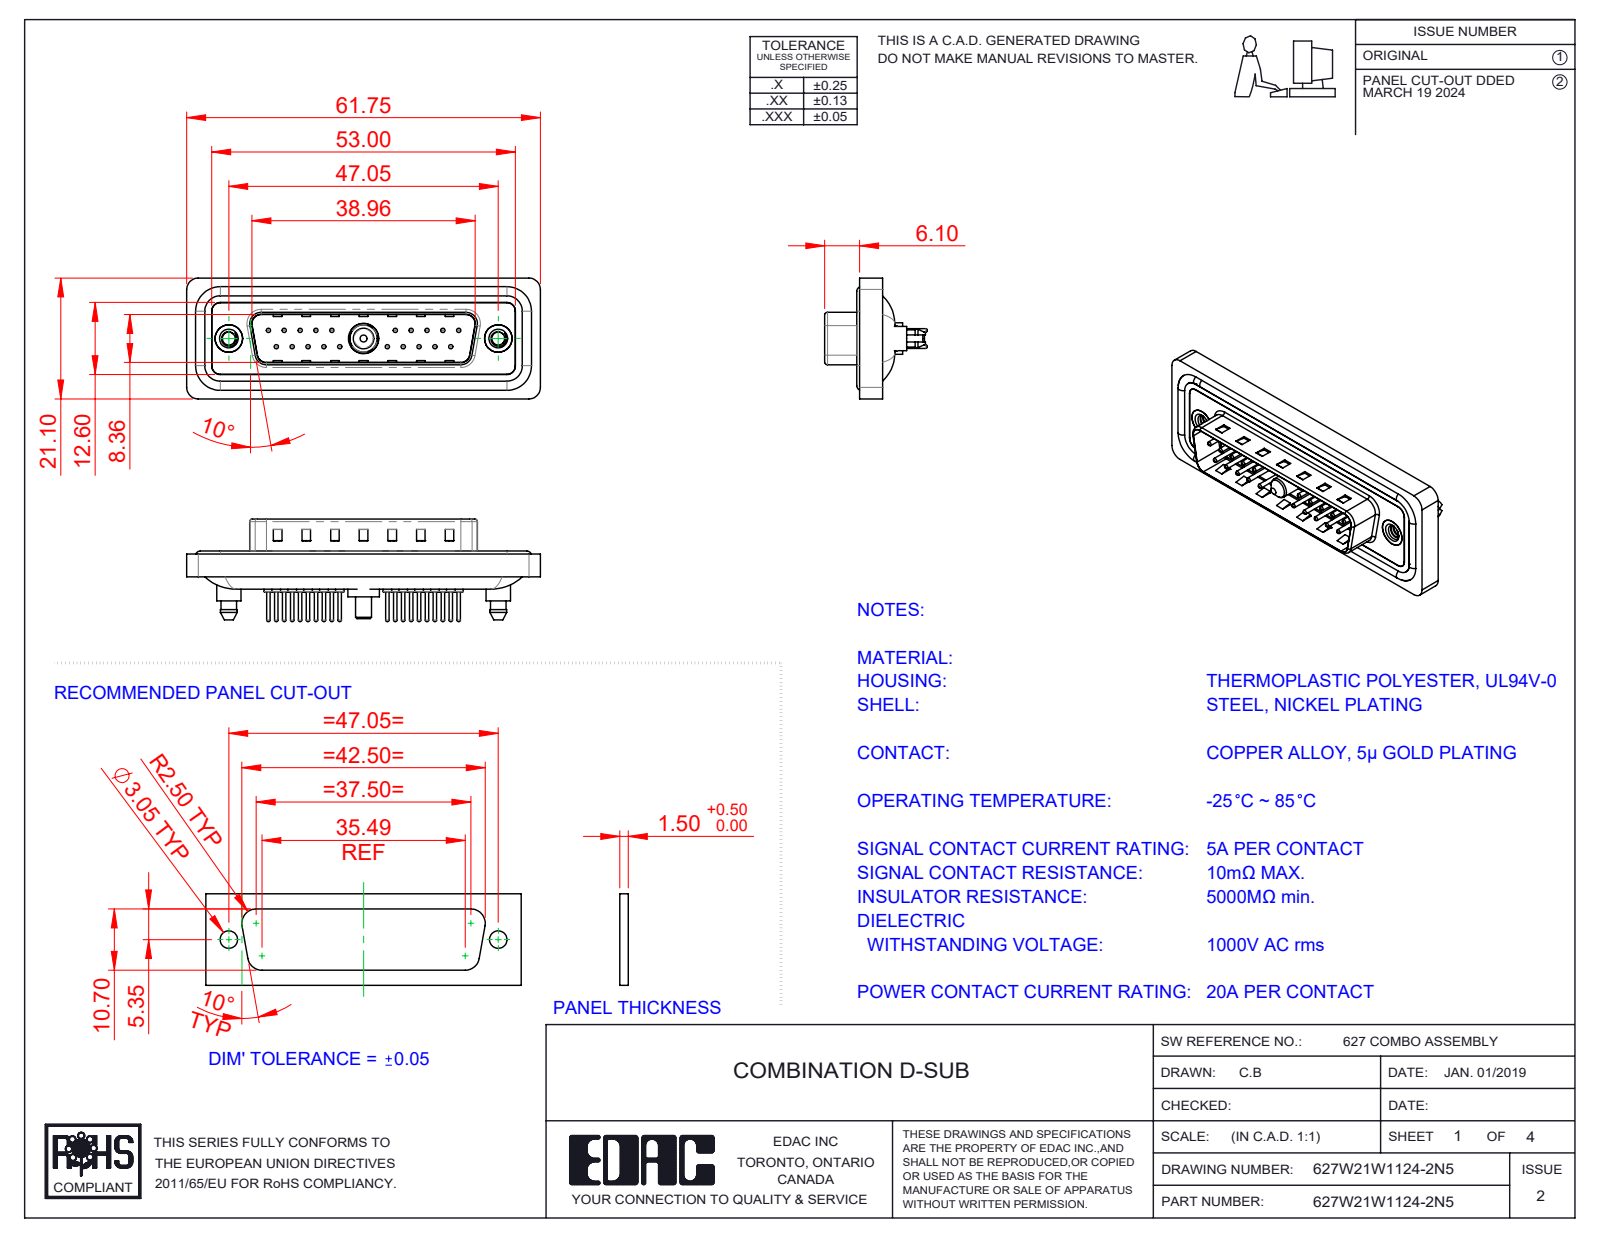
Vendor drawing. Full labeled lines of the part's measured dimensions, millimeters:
Part name (STEP PRODUCT): 627Combo Shell Rear_25 Contacts; Power Pin_20A S; 627Combo Housing_21W1; 627Combo Threaded Boardlock_5 (+5 more)
STEP written by: SolidWorks 2023 (CONFIG_CONTROL_DESIGN)
Units: millimetres
Bodies: 29 solids, 1312 faces (375 planar, 519 cylindrical, 418 other)
Overall size (bounding box): 61.75 × 21.1 × 17.9
Volume: 7 331 mm³ · Surface area: 12 286 mm²
Round holes (diameter × count): ⌀0.75 ×20, ⌀1.6 ×20, ⌀2 ×20, ⌀2.26 ×2, ⌀4 ×2, ⌀4.8 ×2, ⌀5 ×2, ⌀4.85 ×1, ⌀5.3 ×1
Round bosses / shafts (diameter × count): ⌀1.5 ×20, ⌀0.6 ×20, ⌀1.6 ×4, ⌀5.4 ×2, ⌀4.9 ×2, ⌀4.25 ×2, ⌀5.5 ×1, ⌀5.2 ×1
Partial cylindrical surfaces — rounded edges, fillets, slot ends (radius × count): R1.5 ×24, R2 ×18, R1.6 ×10, R0.5 ×8, R0.25 ×4, R0.6 ×4, R0.65 ×4, R0.9 ×4
Main face-to-face distances: 0.4, 1.5, 1.1, 1.6, 0.5, 3.1, 2.9, 4.1, 0.82, 9.58
Hole centre spacings: 3.16, 2.77, 5.54, 8.31, 5.04, 19.39, 20.97, 22.16
